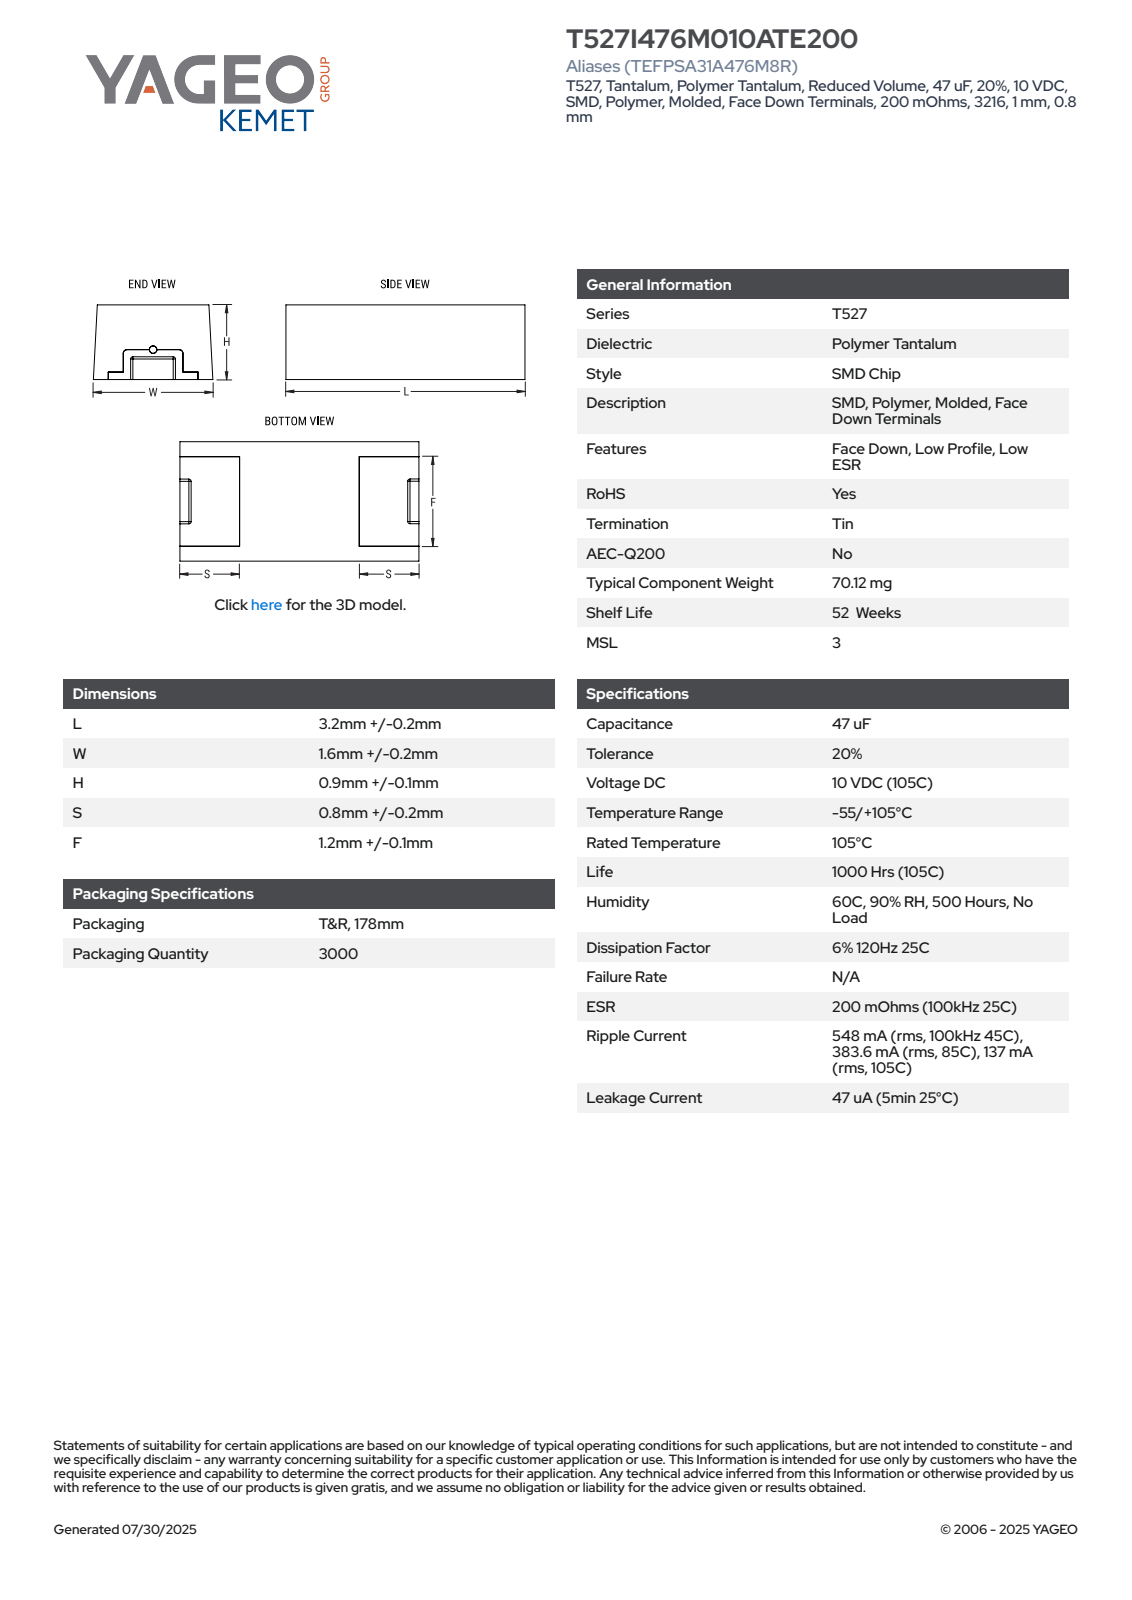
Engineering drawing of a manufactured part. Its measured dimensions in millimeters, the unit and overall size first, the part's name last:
Units: millimetres
Overall size (bounding box): 3.4 × 1.8 × 1
Partial cylindrical surfaces — rounded edges, fillets, slot ends (radius × count): R0.1 ×4
Main face-to-face distances: 1, 1.8, 3.4, 1.55, 0.8, 2.6, 3.3, 0.7, 2.5, 1.3
Volume: 6 mm³ · Surface area: 24 mm²
Bodies: 4 solids, 107 faces (99 planar, 8 cylindrical, 0 other)
Part name (STEP PRODUCT): CTS_TCBFD_3216_L3.4W1.8H1S0.8F1.3
STEP written by: SolidWorks 2020 (AUTOMOTIVE_DESIGN)
